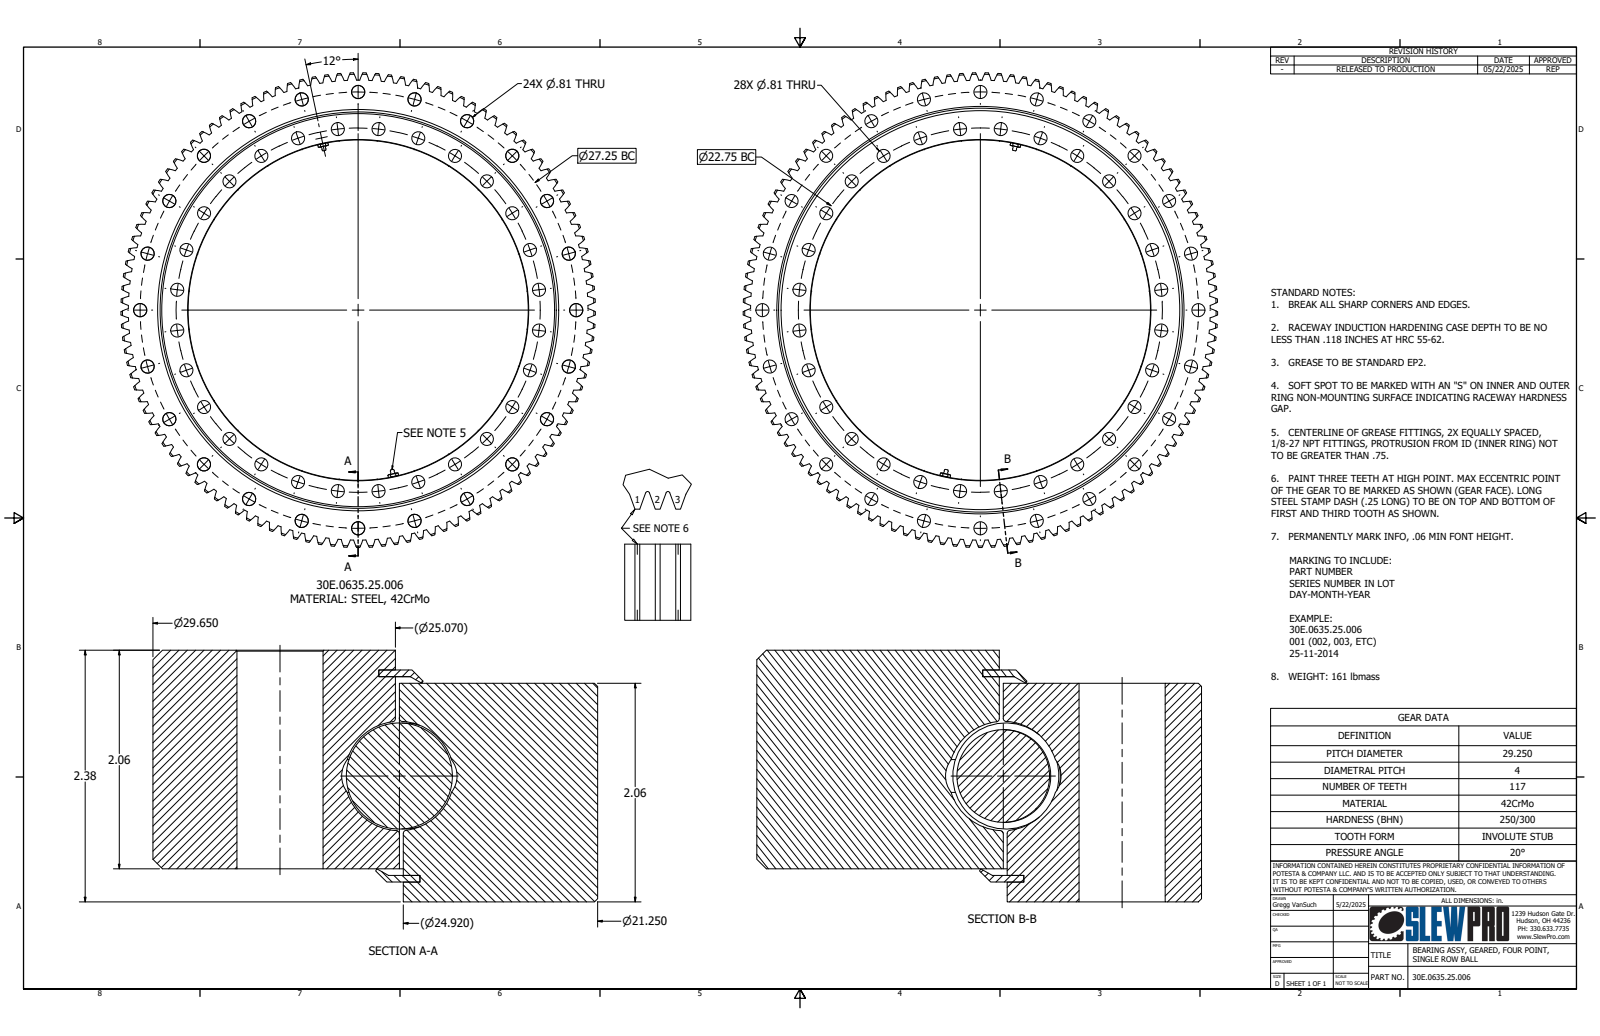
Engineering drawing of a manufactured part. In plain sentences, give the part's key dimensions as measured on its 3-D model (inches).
The part is named "30E.0635.25.000". Its 3-D file was written by "Autodesk Inventor 2026 (AUTOMOTIVE_DESIGN)". It is 6 solids with 979 faces: 16 planar, 536 cylindrical and 427 other. Overall it measures 29.649 by 29.647 by 2.375 inches. Its volume is 577.8 cubic inches and its surface area 2 165 square inches. Round holes: 52 of diameter 0.813, 1 of diameter 1.126, 1 of diameter 21.25, 1 of diameter 24.607, 1 of diameter 24.995, 1 of diameter 25.07, 1 of diameter 25.383. Round bosses or shafts: 1 of diameter 25.383, 1 of diameter 24.92, 1 of diameter 24.607, 1 of diameter 1.125. Partial cylindrical surfaces (rounded edges, fillets, slot ends): 234 of radius 2.706, 1 of radius 14.363, 1 of radius 14.825. The main face-to-face distances are 2.063, 0.312, 1.751, 2.375, 1.939, 0.063, 0.187, 2.188, 0.125, 1.876. The hole center spacings are 13.625, 7.053, 25.176, 26.321, 3.557, 10.428, 16.589, 19.269.
